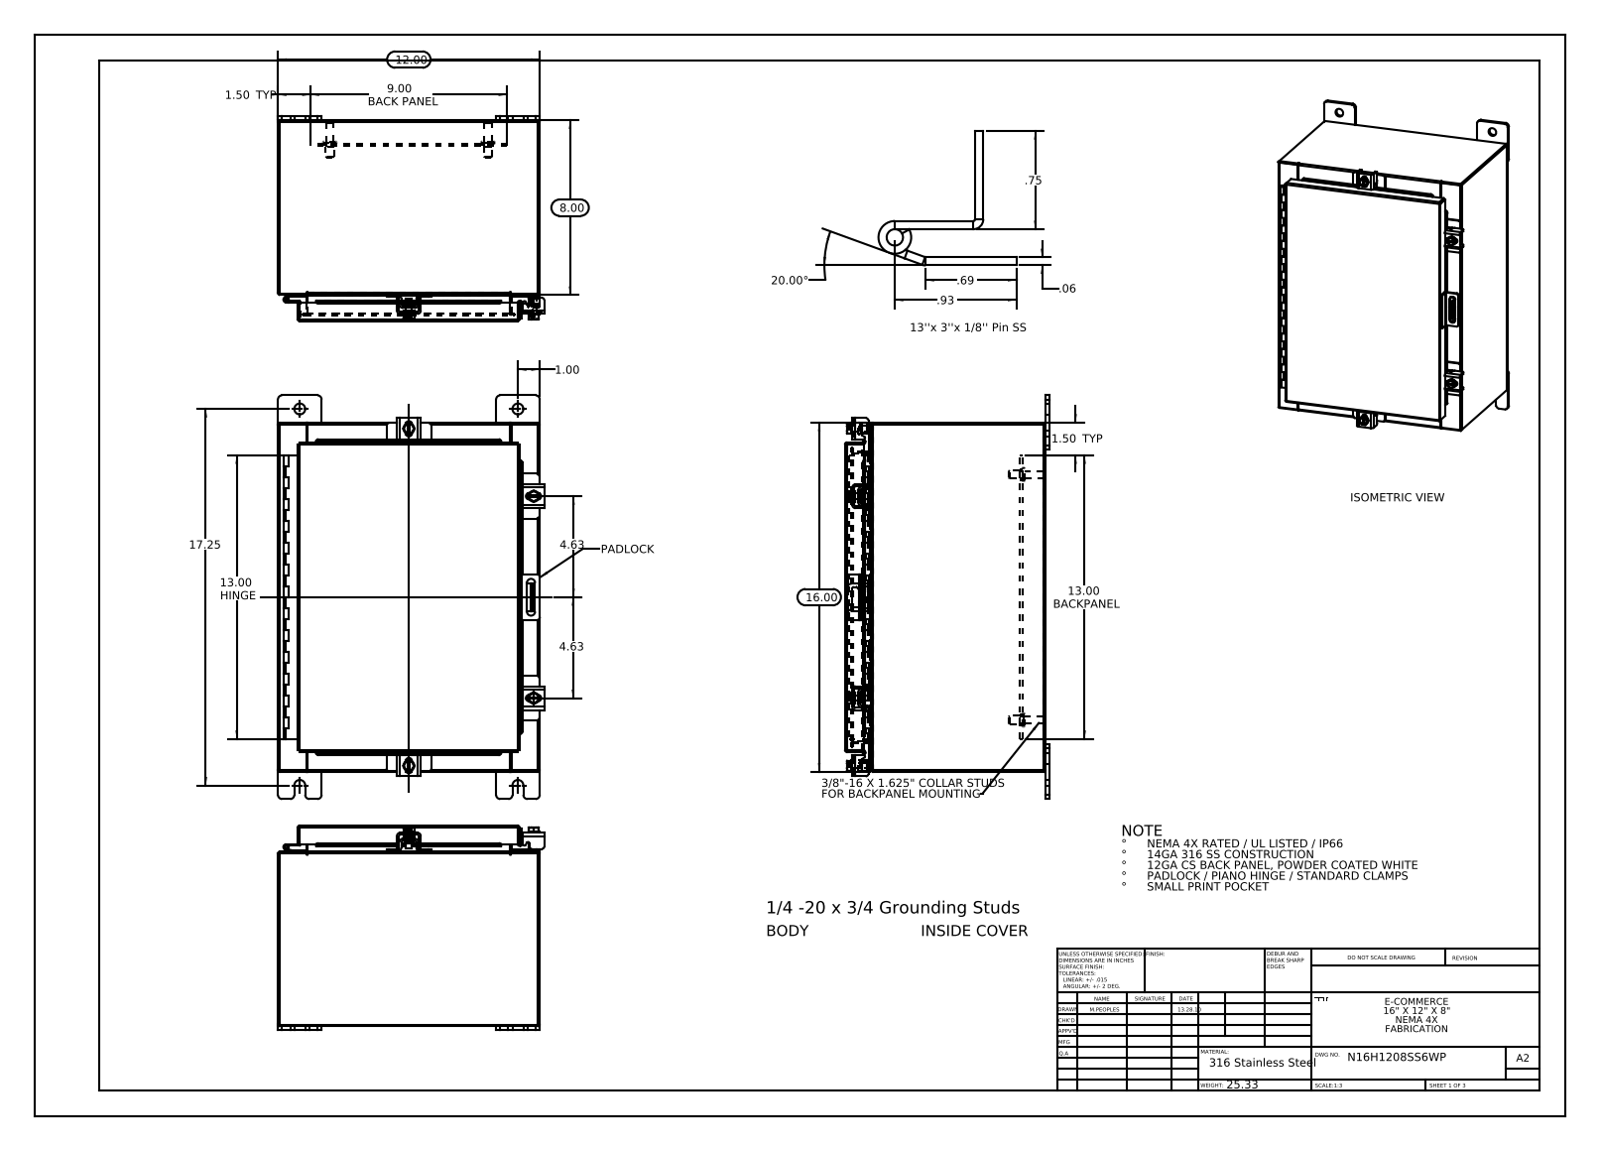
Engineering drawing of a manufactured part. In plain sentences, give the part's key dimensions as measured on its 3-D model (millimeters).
The part is named "N16H1208SS6WP; N16H1208SS6WP Clamp Top; N16H1208SS6WP Padlock Hasp; N16H1208SS6WP Backpanel (+8 more)". Its 3-D file was written by "SolidWorks 2013 (CONFIG_CONTROL_DESIGN)". It is 37 solids with 1267 faces: 680 planar, 507 cylindrical and 80 other. Overall it measures 469.9 by 310.2 by 238.5 millimeters. Its volume is 1 469 000 cubic millimeters and its surface area 1 480 000 square millimeters. Round holes: 8 of diameter 12.7, 4 of diameter 5.4, 4 of diameter 6.6, 2 of diameter 3.2, 1 of diameter 3.2. Round bosses or shafts: 5 of diameter 6.4, 4 of diameter 15.9, 4 of diameter 12.7, 4 of diameter 10.1, 4 of diameter 9.5, 4 of diameter 8.4. Partial cylindrical surfaces (rounded edges, fillets, slot ends): 24 of radius 4.8, 23 of radius 0.3, 22 of radius 1.5, 21 of radius 2.2, 10 of radius 3.2, 8 of radius 3, 8 of radius 3.6, 7 of radius 1.3. The main face-to-face distances are 1.9, 231.8, 302.9, 404.5, 233.7, 229.9, 201.3, 30.5, 301, 304.8. The hole center spacings are 351.4, 56.5, 59.1, 83.8, 106.4, 106.4, 127.3, 129.
